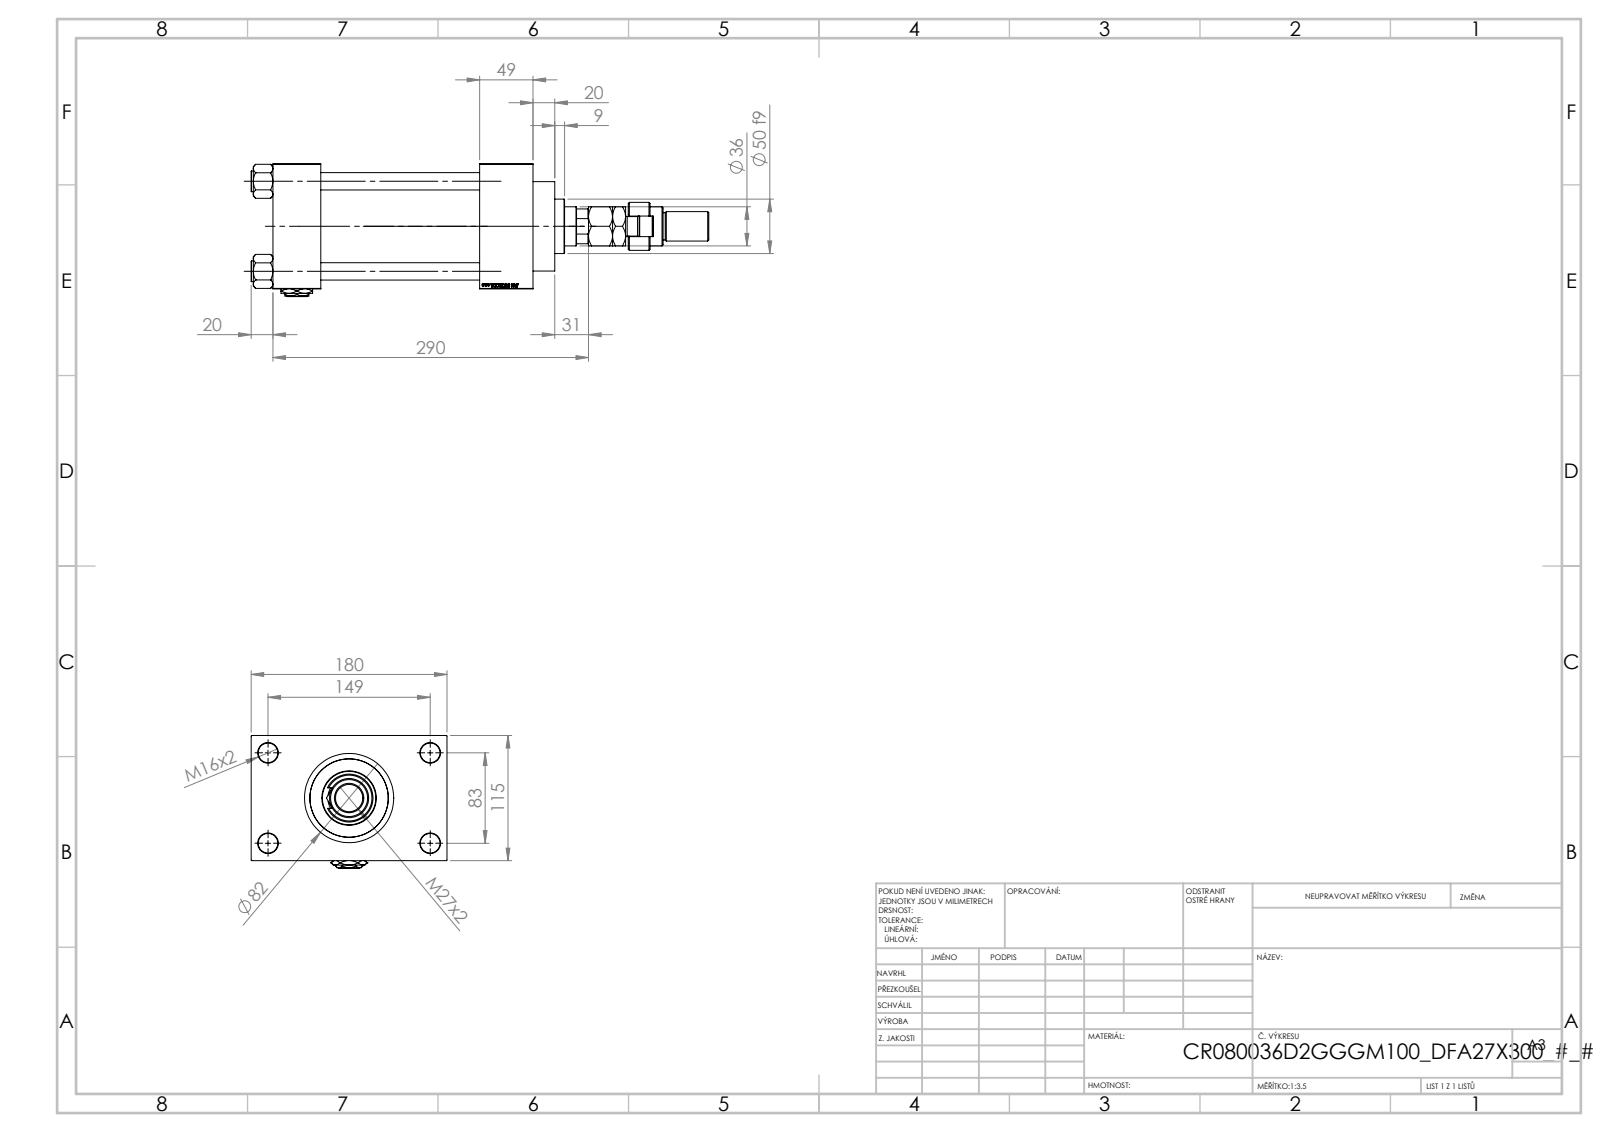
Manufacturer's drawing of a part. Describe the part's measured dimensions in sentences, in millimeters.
The part is named "V215_VC_A; V215CR_D_TYCINKA; V215CR_D_Body; V215CR_VCP_D (+4 more)". Its 3-D file was written by "SolidWorks 2019 (CONFIG_CONTROL_DESIGN)". It is 14 solids with 1290 faces: 597 planar, 109 cylindrical and 584 other. Overall it measures 420.5 by 180 by 122 millimeters. Its volume is 2 300 000 cubic millimeters and its surface area 385 662 square millimeters. Round holes: 4 of diameter 16, 4 of diameter 18, 2 of diameter 7, 2 of diameter 26.44, 2 of diameter 35, 1 of diameter 25.5, 1 of diameter 39, 1 of diameter 61, 1 of diameter 72, 1 of diameter 80. Round bosses or shafts: 4 of diameter 19, 1 of diameter 86, 1 of diameter 82, 1 of diameter 50, 1 of diameter 44, 1 of diameter 36, 1 of diameter 28, 1 of diameter 27. Partial cylindrical surfaces (rounded edges, fillets, slot ends): 1 of radius 9.5, 1 of radius 15, 1 of radius 17.5. The main face-to-face distances are 115, 146, 195, 49, 44, 190, 239, 32.5, 147.5, 180. The hole center spacings are 33.15, 58.48, 82.7, 85.28, 89.24, 115.85, 142.43, 83.
